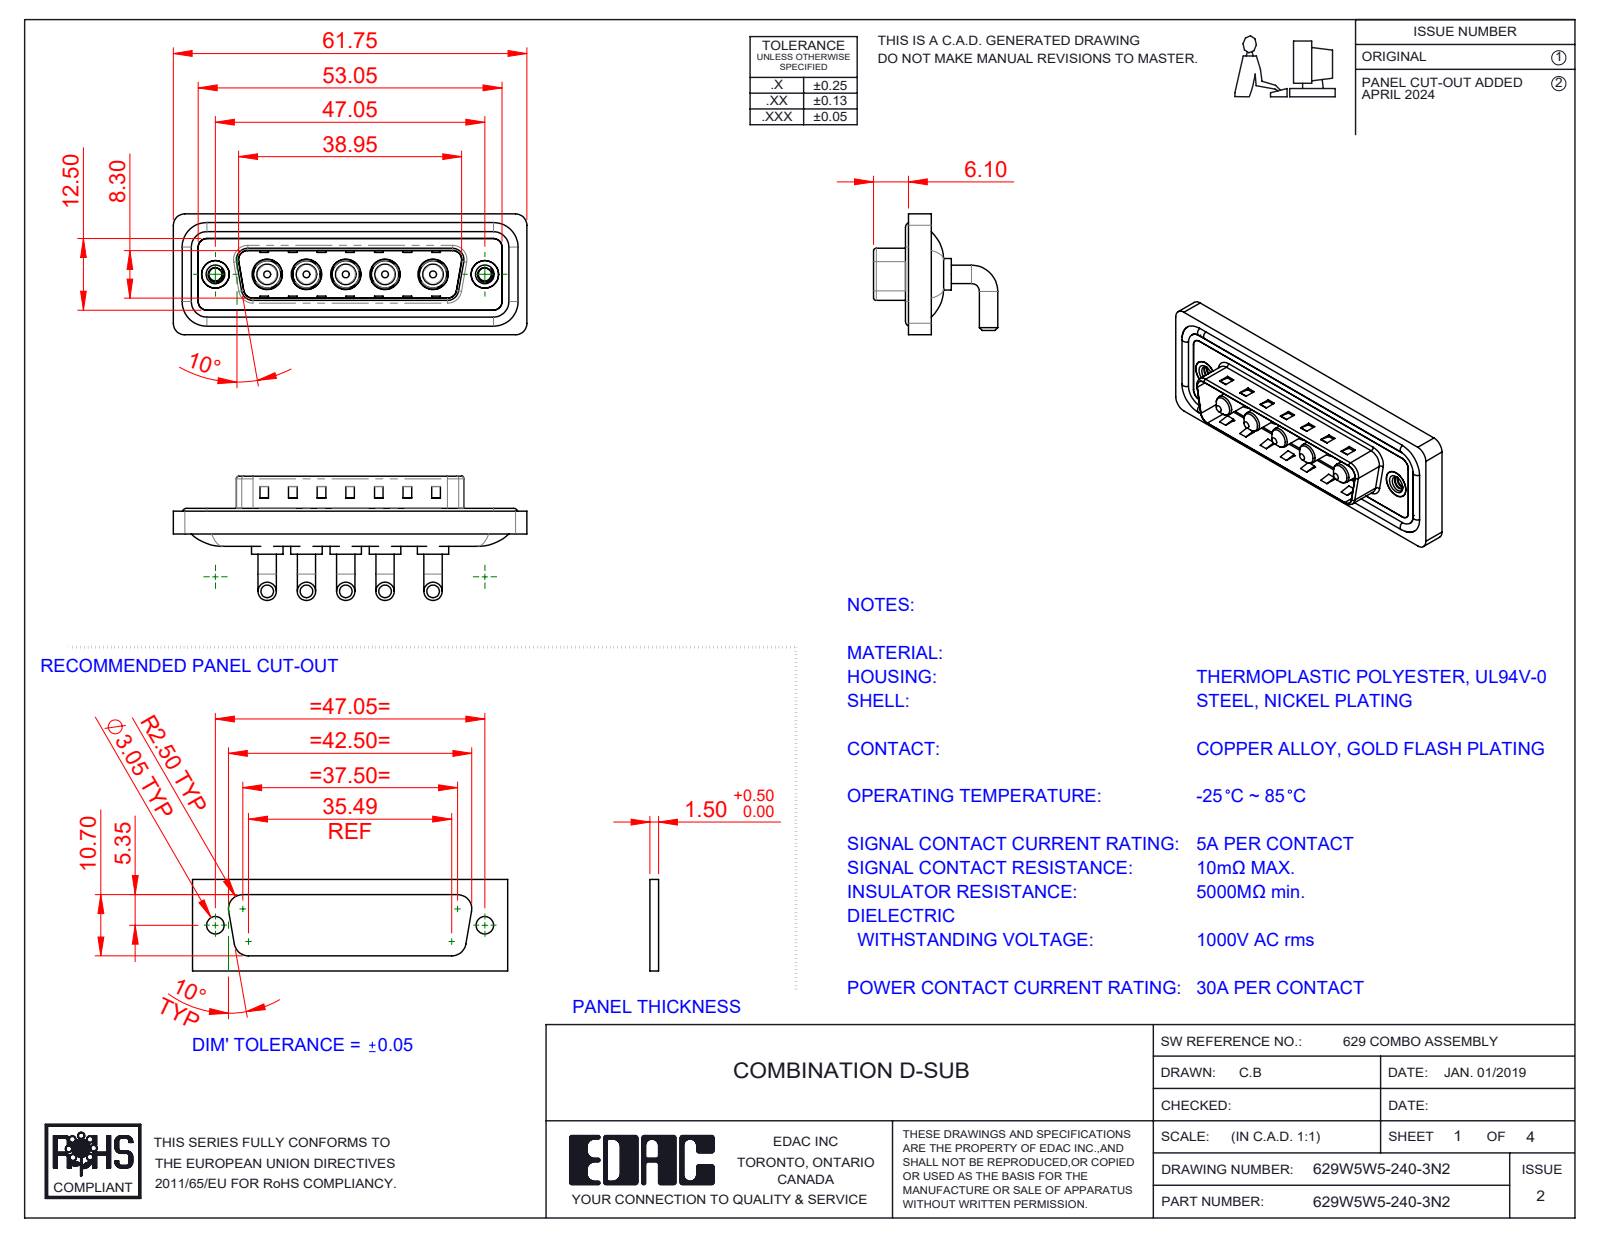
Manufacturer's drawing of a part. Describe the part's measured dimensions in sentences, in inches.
The part is named "629Combo Threaded Rivet_2; 629Combo Shell Front_25 Contacts; 629W5W5-240-3N2; Power Pin_30A RA (+3 more)". Its 3-D file was written by "SolidWorks 2023 (CONFIG_CONTROL_DESIGN)". It is 17 solids with 698 faces: 259 planar, 293 cylindrical and 146 other. Overall it measures 2.431 by 0.854 by 0.831 inches. Its volume is 0.485 cubic inches and its surface area 19.16 square inches. Round holes: 5 of diameter 0.191, 5 of diameter 0.209, 2 of diameter 0.089, 2 of diameter 0.157, 2 of diameter 0.189, 2 of diameter 0.197. Round bosses or shafts: 10 of diameter 0.126, 5 of diameter 0.217, 5 of diameter 0.205, 5 of diameter 0.187, 5 of diameter 0.148, 5 of diameter 0.142, 4 of diameter 0.063, 2 of diameter 0.193. Partial cylindrical surfaces (rounded edges, fillets, slot ends): 18 of radius 0.059, 18 of radius 0.079, 8 of radius 0.02, 8 of radius 0.063, 5 of radius 0.083, 4 of radius 0.01, 4 of radius 0.024, 4 of radius 0.026. The main face-to-face distances are 0.016, 0.114, 0.031, 0.177, 0.161, 0.043, 0.083, 0.122, 0.236, 0.059. The hole center spacings are 0.27, 0.541, 0.27, 0.27, 0.33, 0.33, 0.356, 0.356.
